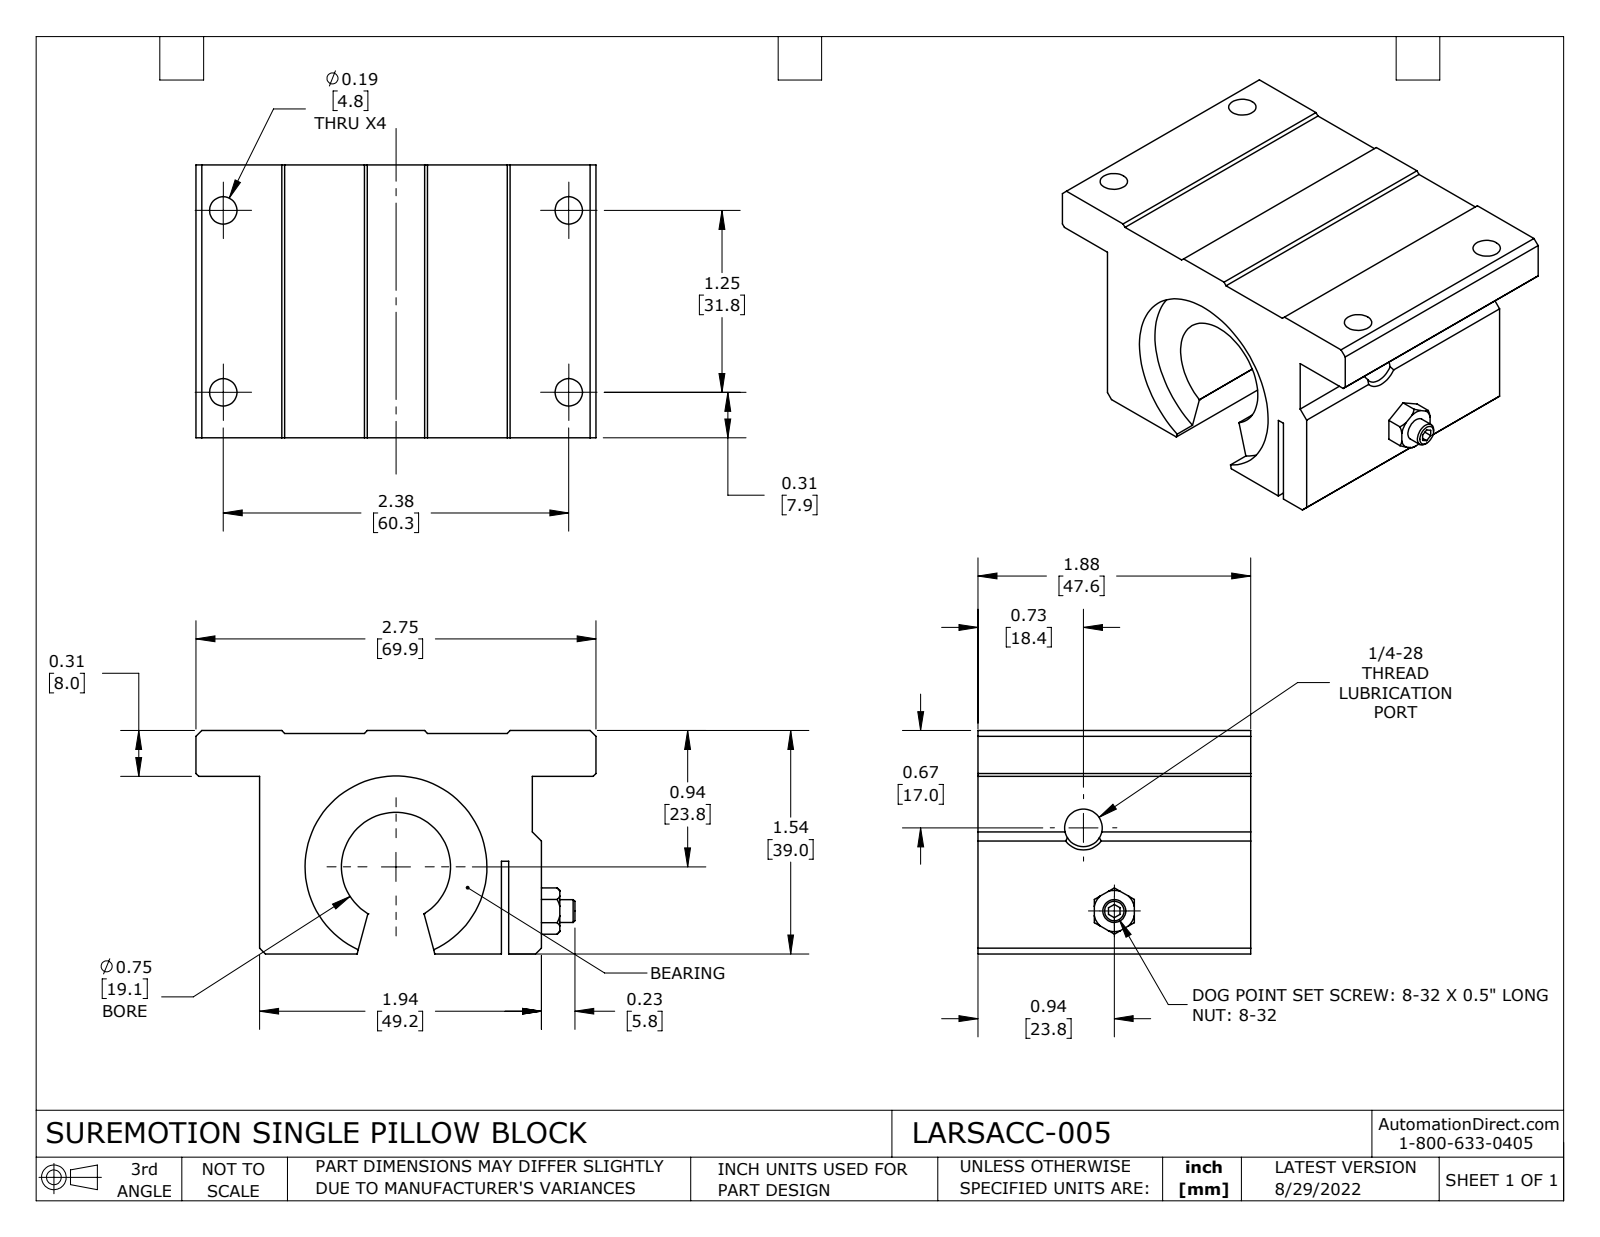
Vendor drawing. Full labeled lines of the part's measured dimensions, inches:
Part name (STEP PRODUCT): LARSACC-005
STEP written by: SolidWorks 2021 (CONFIG_CONTROL_DESIGN)
Units: inches
Bodies: 1 solid, 85 faces (54 planar, 21 cylindrical, 10 other)
Overall size (bounding box): 2.75 × 1.875 × 1.535
Volume: 4.618 in³ · Surface area: 28.58 in²
Round holes (diameter × count): ⌀0.188 ×4, ⌀0.258 ×1, ⌀0.75 ×1, ⌀1.25 ×1
Round bosses / shafts (diameter × count): ⌀0.157 ×1
Main face-to-face distances: 1.535, 1.515, 0.02, 1.875, 1.22, 0.295, 0.315, 0.15, 1.725, 1.937
Hole centre spacings: 1.25, 2.376, 2.684
